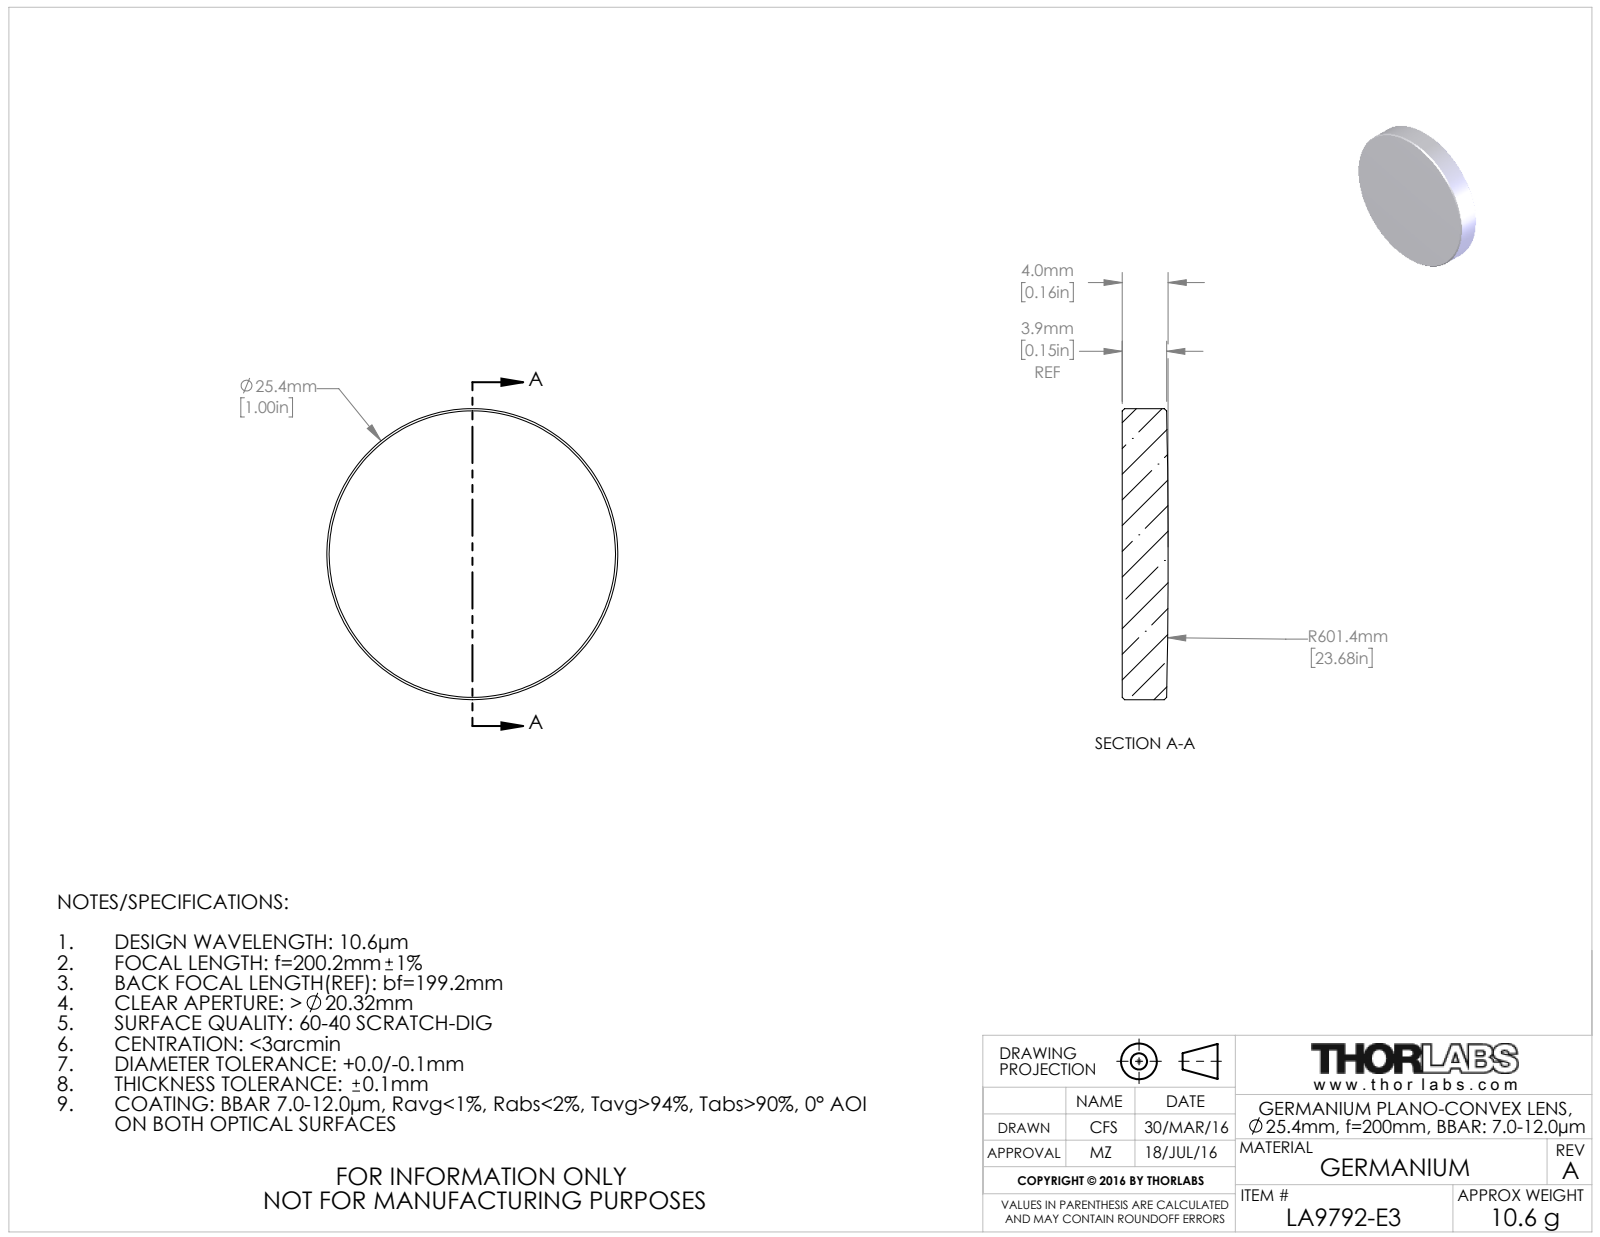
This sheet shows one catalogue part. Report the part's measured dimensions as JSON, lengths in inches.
{"part_name": "TTN049381-E0W", "step_written_by": "SolidWorks 2016 (CONFIG_CONTROL_DESIGN)", "units": "inches", "bodies": {"solids": 1, "faces": 9, "planar": 1, "cylindrical": 2, "other": 6}, "overall_size": [1, 1, 0.157], "volume_in3": 0.121, "surface_area_in2": 2.02, "round_bosses_or_shafts": [[1, 1]]}
